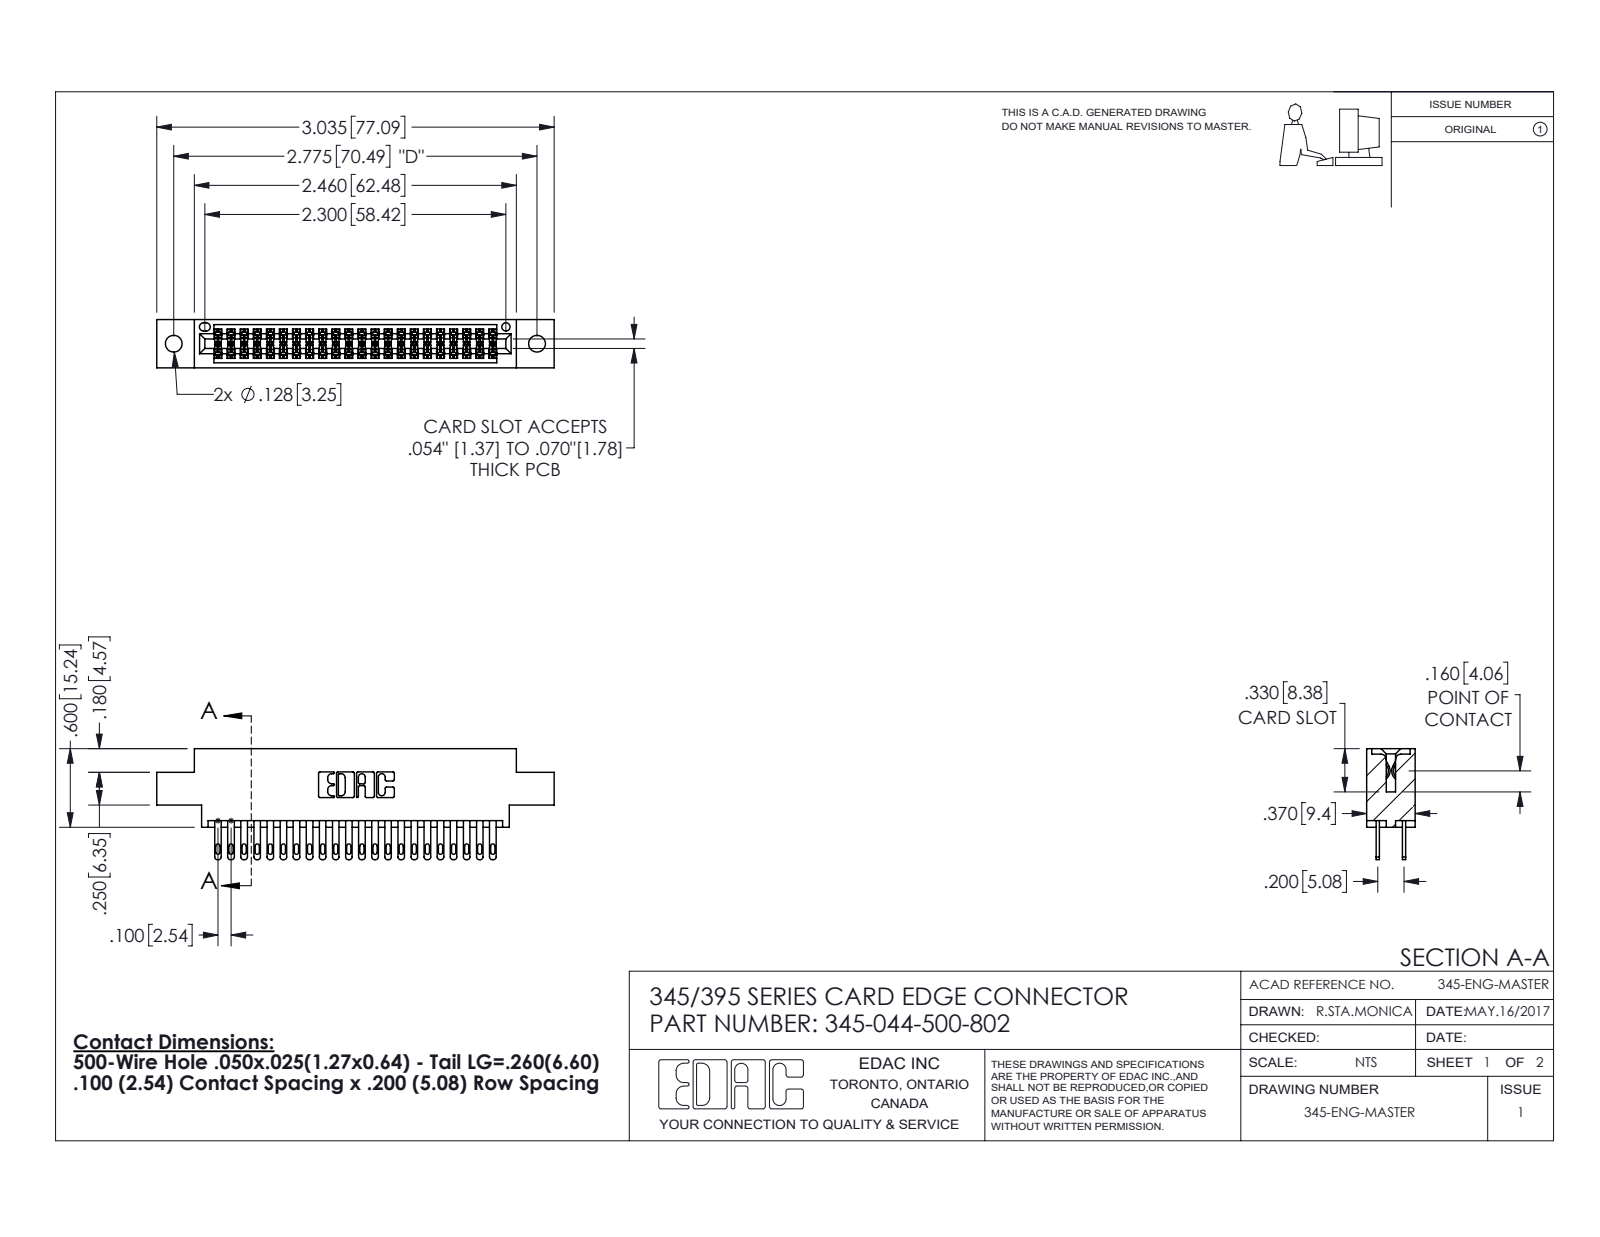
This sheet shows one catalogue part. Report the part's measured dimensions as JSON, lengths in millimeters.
{"part_name": "345 Part_0.170 Offset - 0.128 Dia; 345-044-500-802; 345-292-001_345-293-100", "step_written_by": "SolidWorks 2016 (CONFIG_CONTROL_DESIGN)", "units": "millimeters", "bodies": {"solids": 45, "faces": 2154, "planar": 1272, "cylindrical": 882, "other": 0}, "overall_size": [77.1, 21.5, 9.4], "volume_mm3": 7290, "surface_area_mm2": 10700, "round_holes": [[3.3, 2], [1.6, 1]], "partial_cylinders_radius": [[0.2, 66], [0.4, 44], [0.5, 44], [0.3, 22], [0.2, 6], [0.8, 6], [0.7, 3], [0.4, 2]], "face_to_face_distances": [7.6, 1.8, 5.1, 2.5, 6.9, 0.6, 9.4, 5.7, 4.4, 3.8], "hole_center_spacings": [6.9, 64.5, 70.5]}
